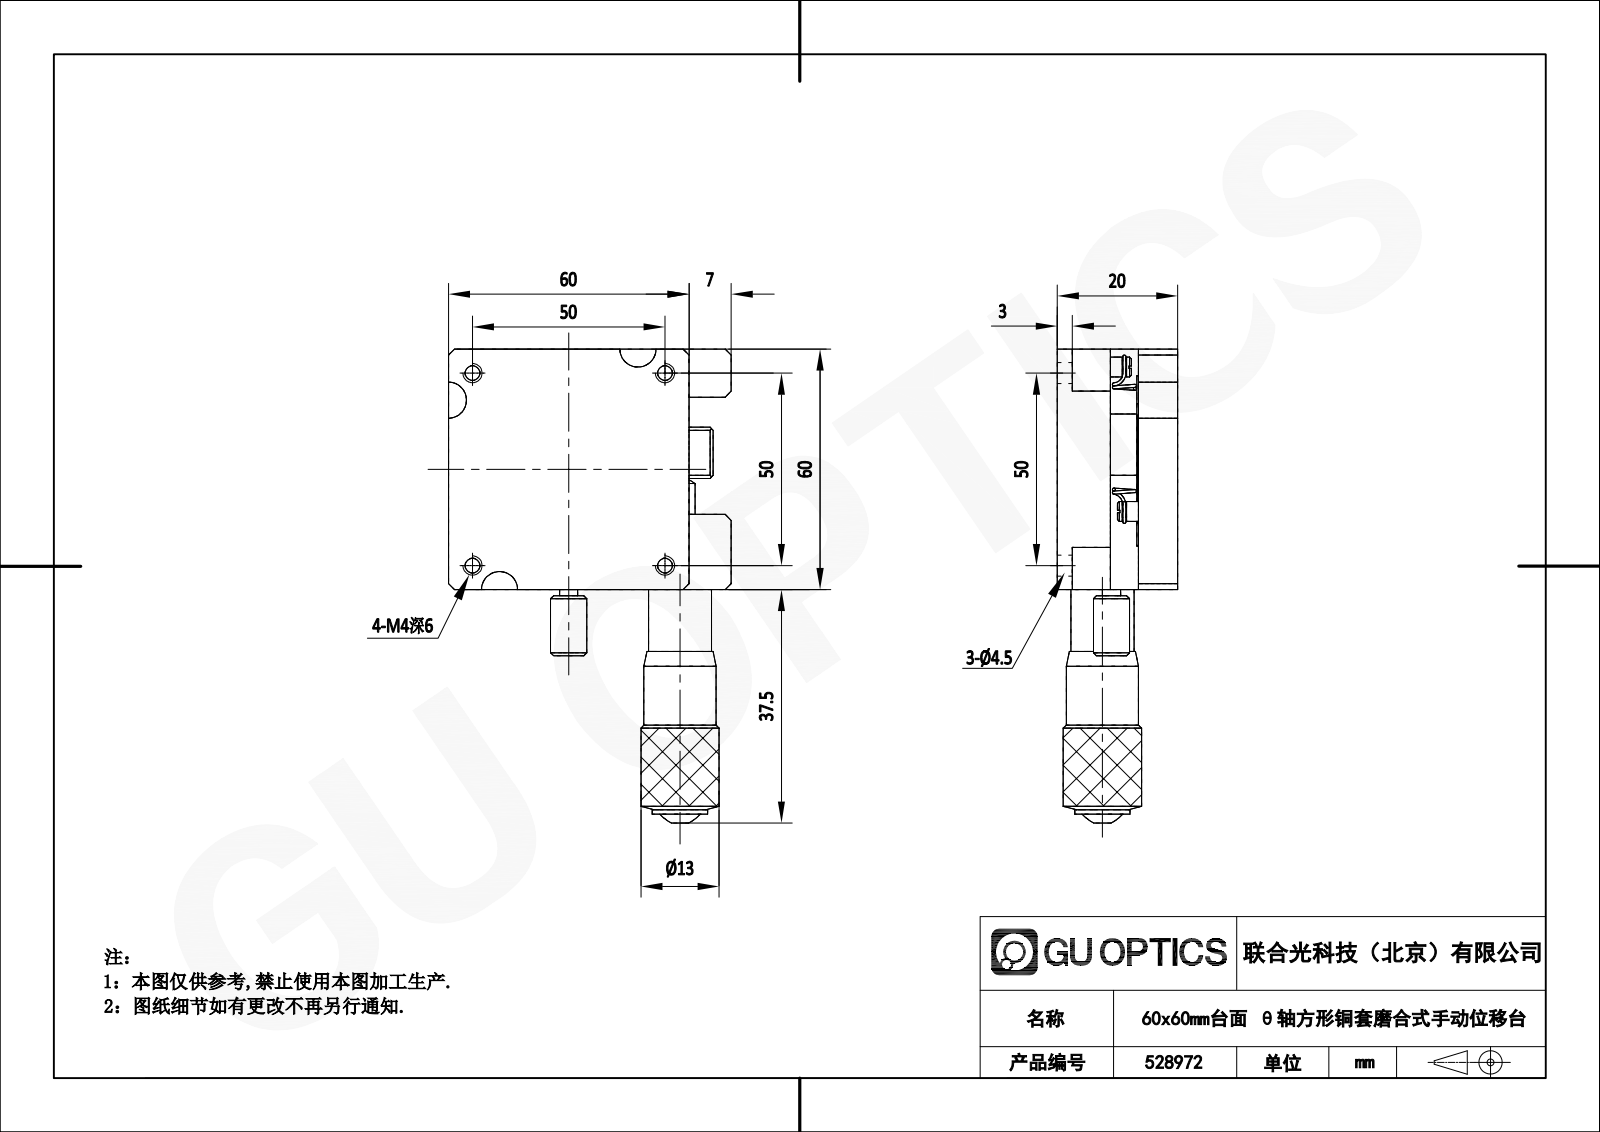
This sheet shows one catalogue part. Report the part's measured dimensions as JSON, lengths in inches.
{"part_name": "528972", "step_written_by": "SolidWorks 2020 (CONFIG_CONTROL_DESIGN)", "units": "inches", "bodies": {"solids": 3, "faces": 2142, "planar": 111, "cylindrical": 485, "other": 1546}, "overall_size": [3.828, 2.716, 0.924], "volume_in3": 3.96, "surface_area_in2": 42.07, "round_holes": [[0.098, 6], [0.062, 4], [0.128, 4], [0.157, 4], [0.177, 3], [0.062, 2], [0.097, 2], [0.097, 1], [0.197, 1], [0.295, 1], [0.354, 1], [0.374, 1]], "round_bosses_or_shafts": [[0.13, 2], [0.079, 2], [1.339, 1], [1.181, 1], [1.142, 1], [0.118, 1], [0.094, 1]], "partial_cylinders_radius": [[0.01, 15], [0.157, 10], [1.024, 4], [0.118, 2], [0.709, 1]], "face_to_face_distances": [0.295, 0.492, 0.787, 2.362, 0.276, 0.472, 0.303, 0.484, 0.197, 0.02], "hole_center_spacings": [1.461, 1.392, 0.445, 0.63, 0.946, 1.837, 1.969, 0.891]}
